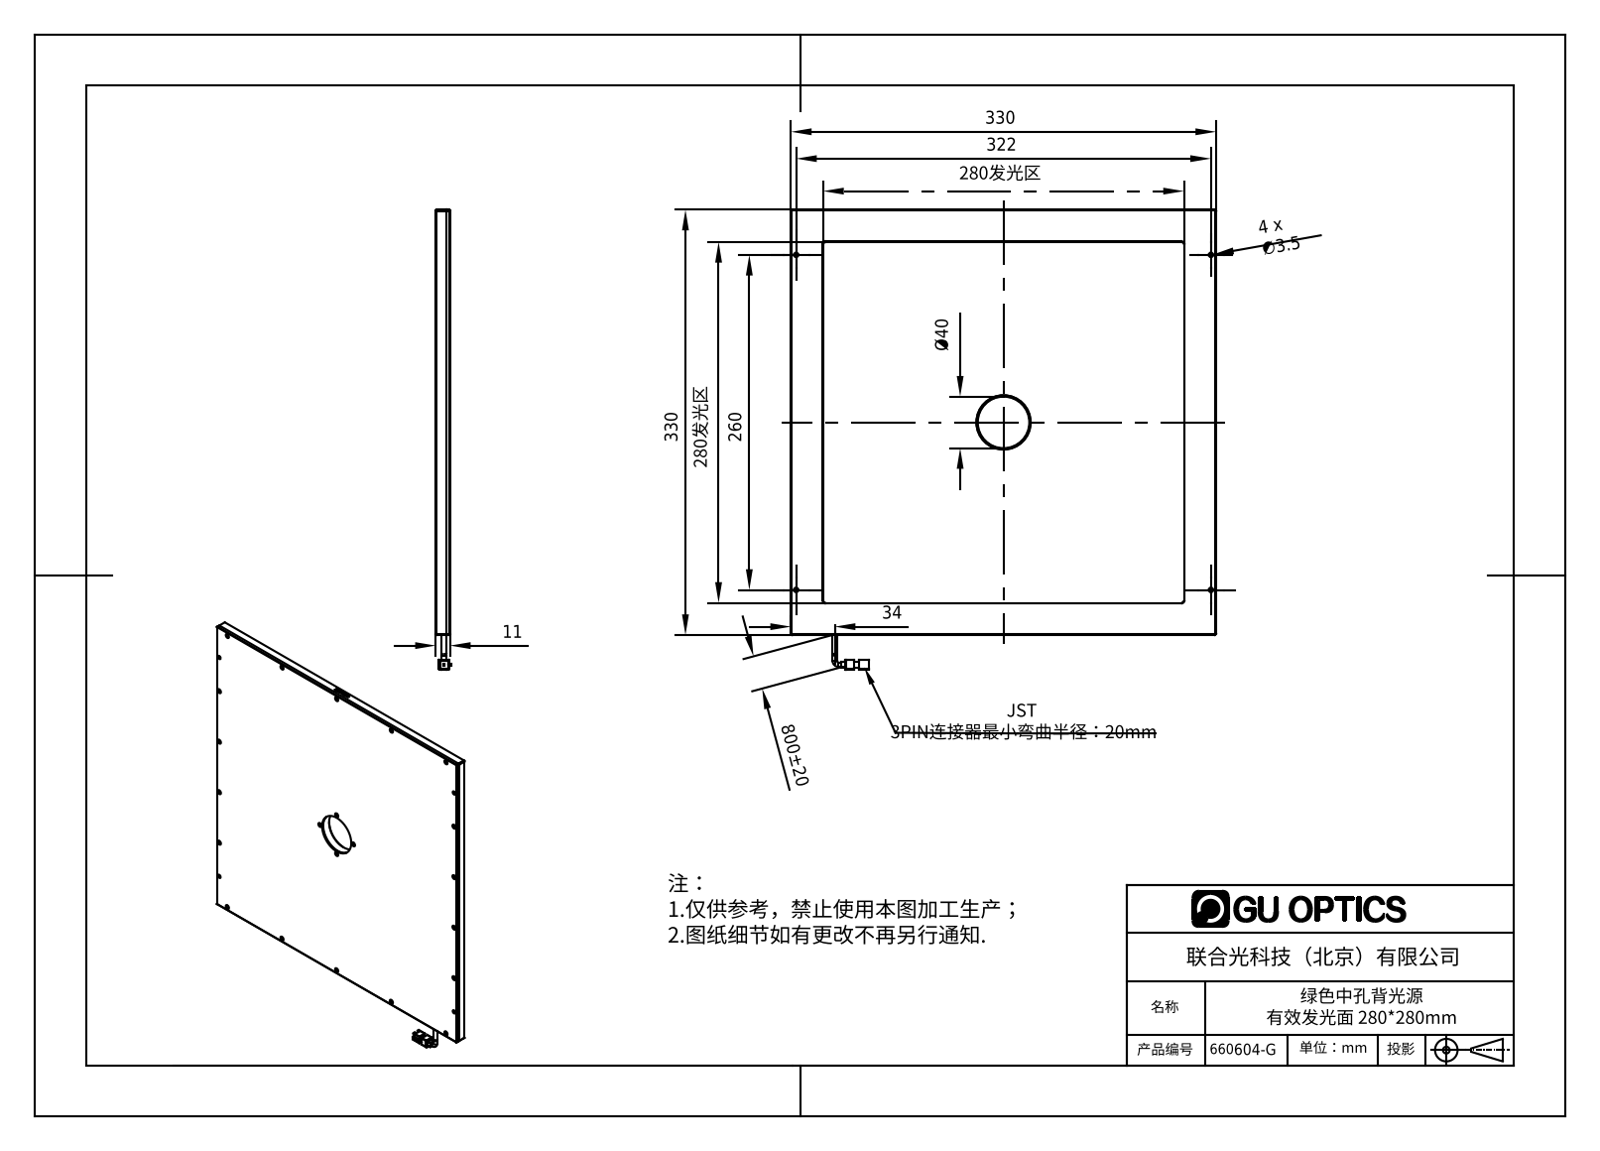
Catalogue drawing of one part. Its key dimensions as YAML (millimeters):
part_name: "660604-G"
step_written_by: "SolidWorks 2016 (AUTOMOTIVE_DESIGN)"
units: millimeters
bodies: {solids: 7, faces: 773, planar: 442, cylindrical: 178, other: 153}
overall_size: [357, 330, 12.4]
volume: 1053000
surface_area: 509529
round_holes:
  - {diameter: 2, count: 22}
  - {diameter: 1.6, count: 18}
  - {diameter: 2.4, count: 18}
  - {diameter: 3.5, count: 5}
  - {diameter: 3.6, count: 4}
  - {diameter: 40, count: 1}
  - {diameter: 42.2, count: 1}
  - {diameter: 52, count: 1}
round_bosses_or_shafts:
  - {diameter: 3.5, count: 2}
  - {diameter: 42, count: 1}
partial_cylinders:
  - {radius: 0.5, count: 8}
  - {radius: 2, count: 8}
  - {radius: 1, count: 4}
  - {radius: 3, count: 2}
face_to_face_distances: [6.5, 9.5, 3, 8, 1.5, 11, 2, 7.5, 322.5, 320.5]
hole_center_spacings: [322, 75, 330.62, 60, 150, 327.54, 355.22, 23]
